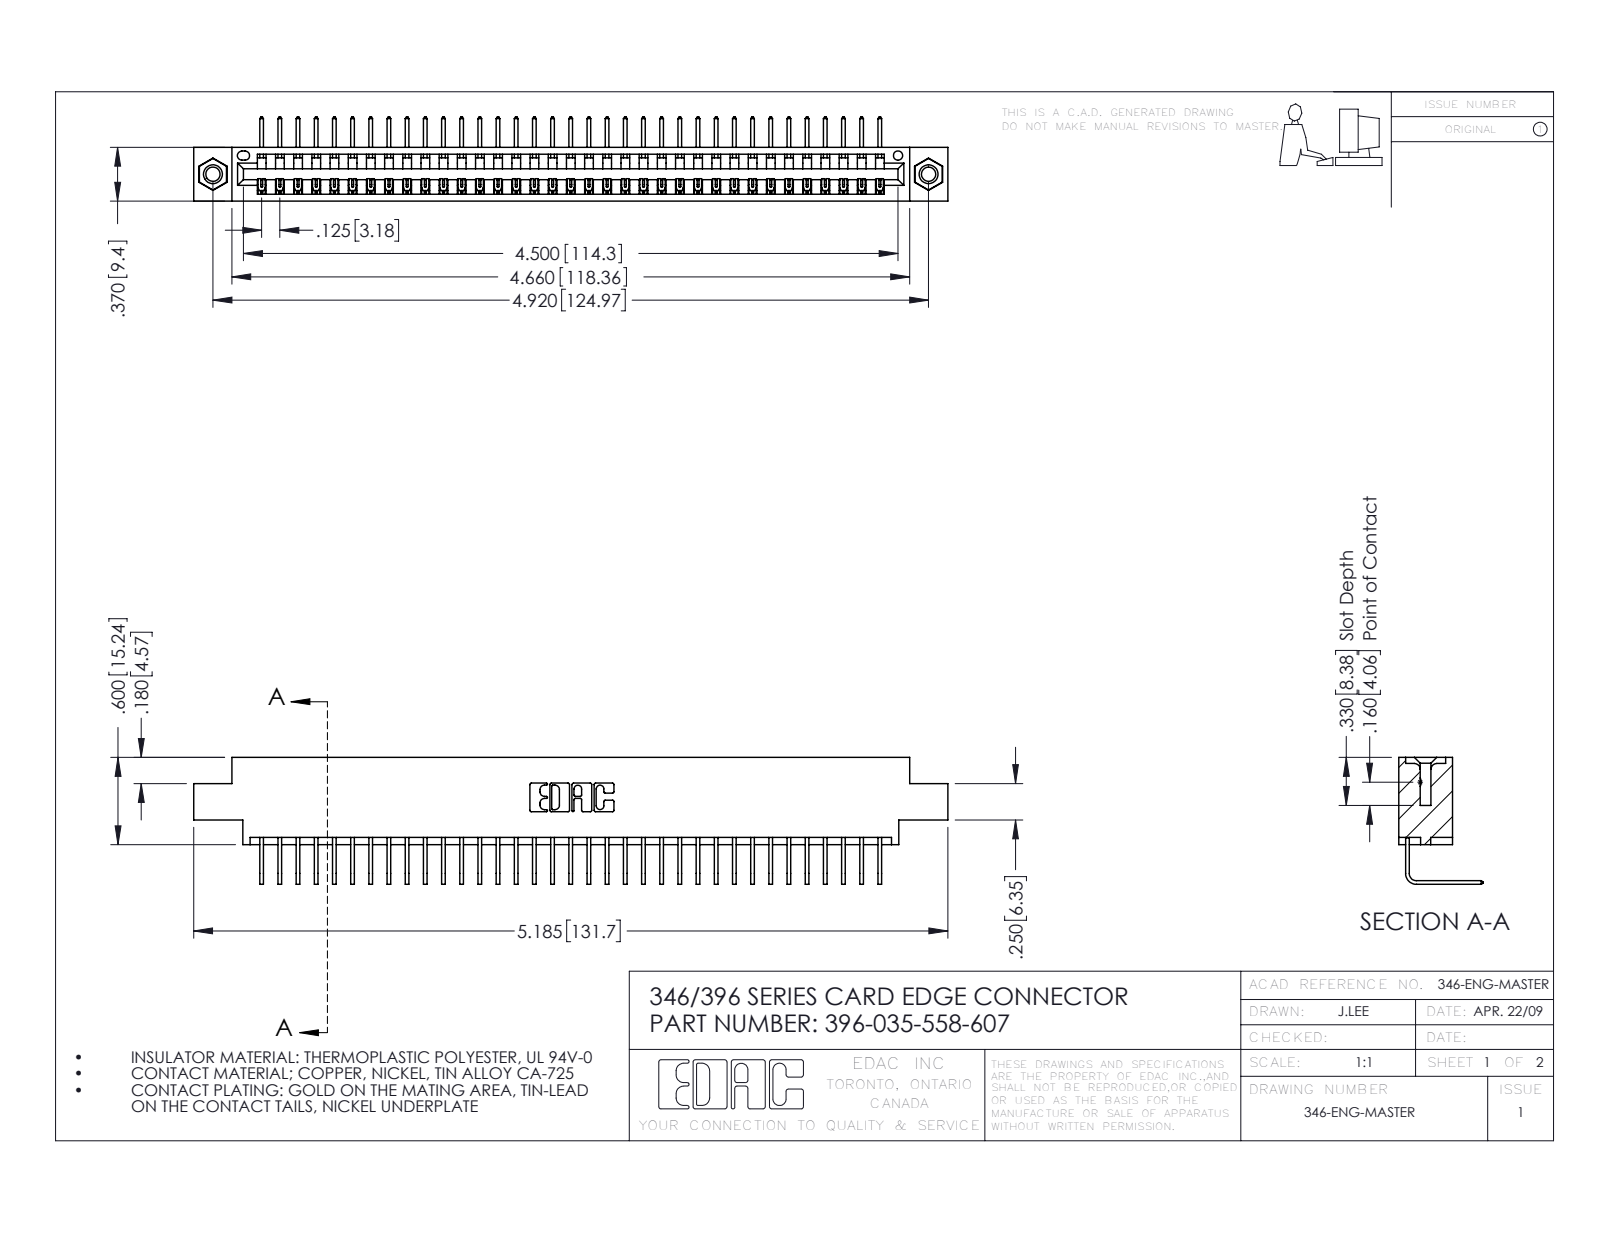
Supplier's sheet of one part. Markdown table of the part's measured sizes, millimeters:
| quantity | value |
| --- | --- |
| part name | 396-035-558-607; 346 Part_0.170 Offset - 0.156 Dia-TI; 345-292-001_558 Tail - 2; 345-250-001_345-250-005-103 |
| STEP written by | SolidWorks 2016 (CONFIG_CONTROL_DESIGN) |
| units | millimeters |
| bodies | 38 solids, 2286 faces (1582 planar, 688 cylindrical, 16 other) |
| overall size | 131.7 × 22.2 × 14.7 |
| volume | 12 500 mm³ |
| surface area | 16 450 mm² |
| round holes (diameter × count) | 2.5 × 2, 3.2 × 2, 4 × 2, 1.6 × 1 |
| round bosses / shafts (diameter × count) | 3.9 × 2 |
| partial cylindrical surfaces (radius × count) | 0.2 × 70, 0.3 × 22, 0.2 × 6, 0.8 × 6, 0.7 × 3, 0.8 × 2, 1 × 2, 0.4 × 1 |
| main face-to-face distances | 8.2, 1.2, 9.4, 6.4, 7.6, 0.6, 1.8, 5.6, 3.8, 2.5 |
| hole center spacings | 6.2, 119.7, 125 |
